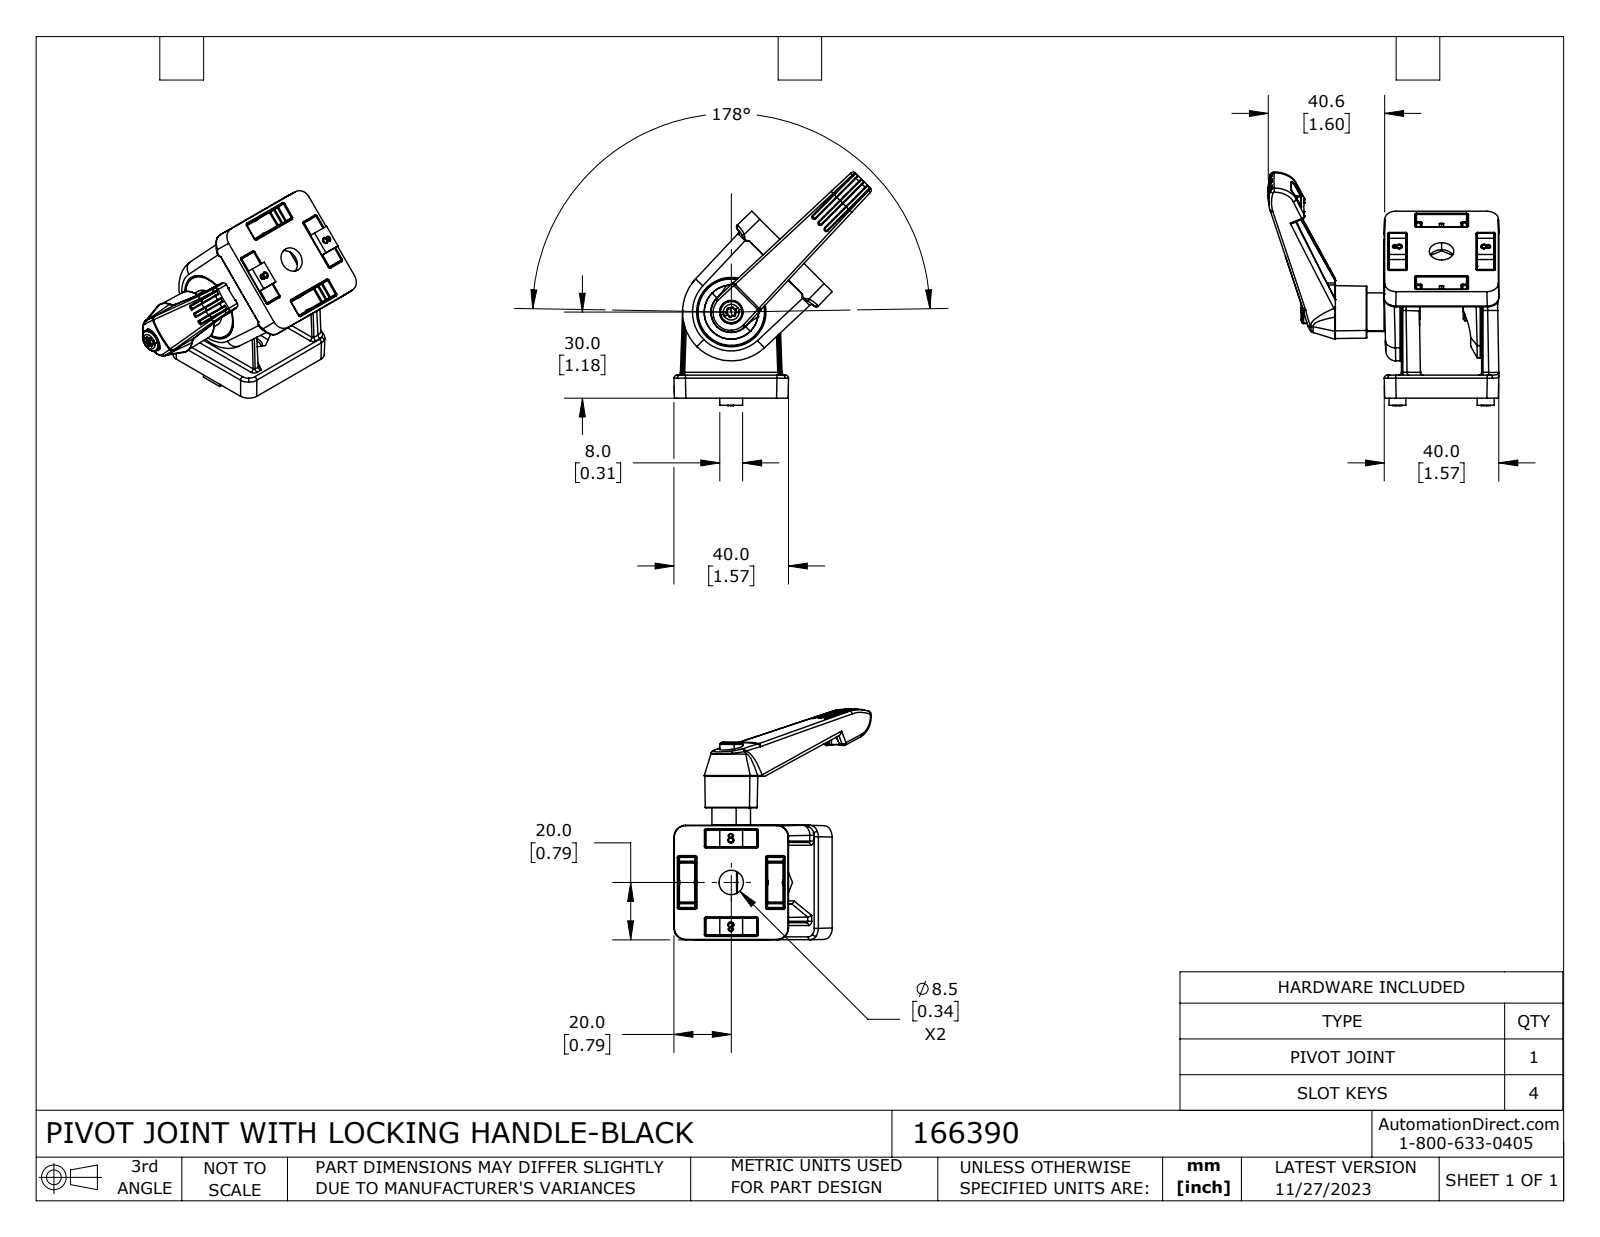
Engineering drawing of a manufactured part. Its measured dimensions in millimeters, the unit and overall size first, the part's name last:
Units: millimetres
Overall size (bounding box): 81.56 × 81.33 × 68.91
Round holes (diameter × count): ⌀2 ×2, ⌀5 ×1, ⌀5.6 ×1, ⌀6.4 ×1, ⌀8.2 ×1, ⌀12.2 ×1, ⌀13 ×1, ⌀14 ×1, ⌀16.2 ×1, ⌀24 ×1, ⌀24.23 ×1, ⌀26 ×1
Round bosses / shafts (diameter × count): ⌀34 ×1, ⌀32 ×1, ⌀25.8 ×1, ⌀23.6 ×1, ⌀16 ×1, ⌀13.5 ×1, ⌀12 ×1, ⌀8 ×1
Partial cylindrical surfaces — rounded edges, fillets, slot ends (radius × count): R0.3 ×156, R0.2 ×44, R1 ×26, R0.5 ×21, R4 ×8, R0.4 ×6, R3.5 ×4, R0.1 ×3
Main face-to-face distances: 8, 28, 30.8, 1, 5.57, 33.57, 5.5, 33.5, 7, 7.56
Hole centre spacings: 10.5, 21
Volume: 52 055 mm³ · Surface area: 35 158 mm²
Bodies: 14 solids, 1713 faces (380 planar, 489 cylindrical, 844 other)
Part name (STEP PRODUCT): 166390
STEP written by: SolidWorks 2023 (CONFIG_CONTROL_DESIGN)
